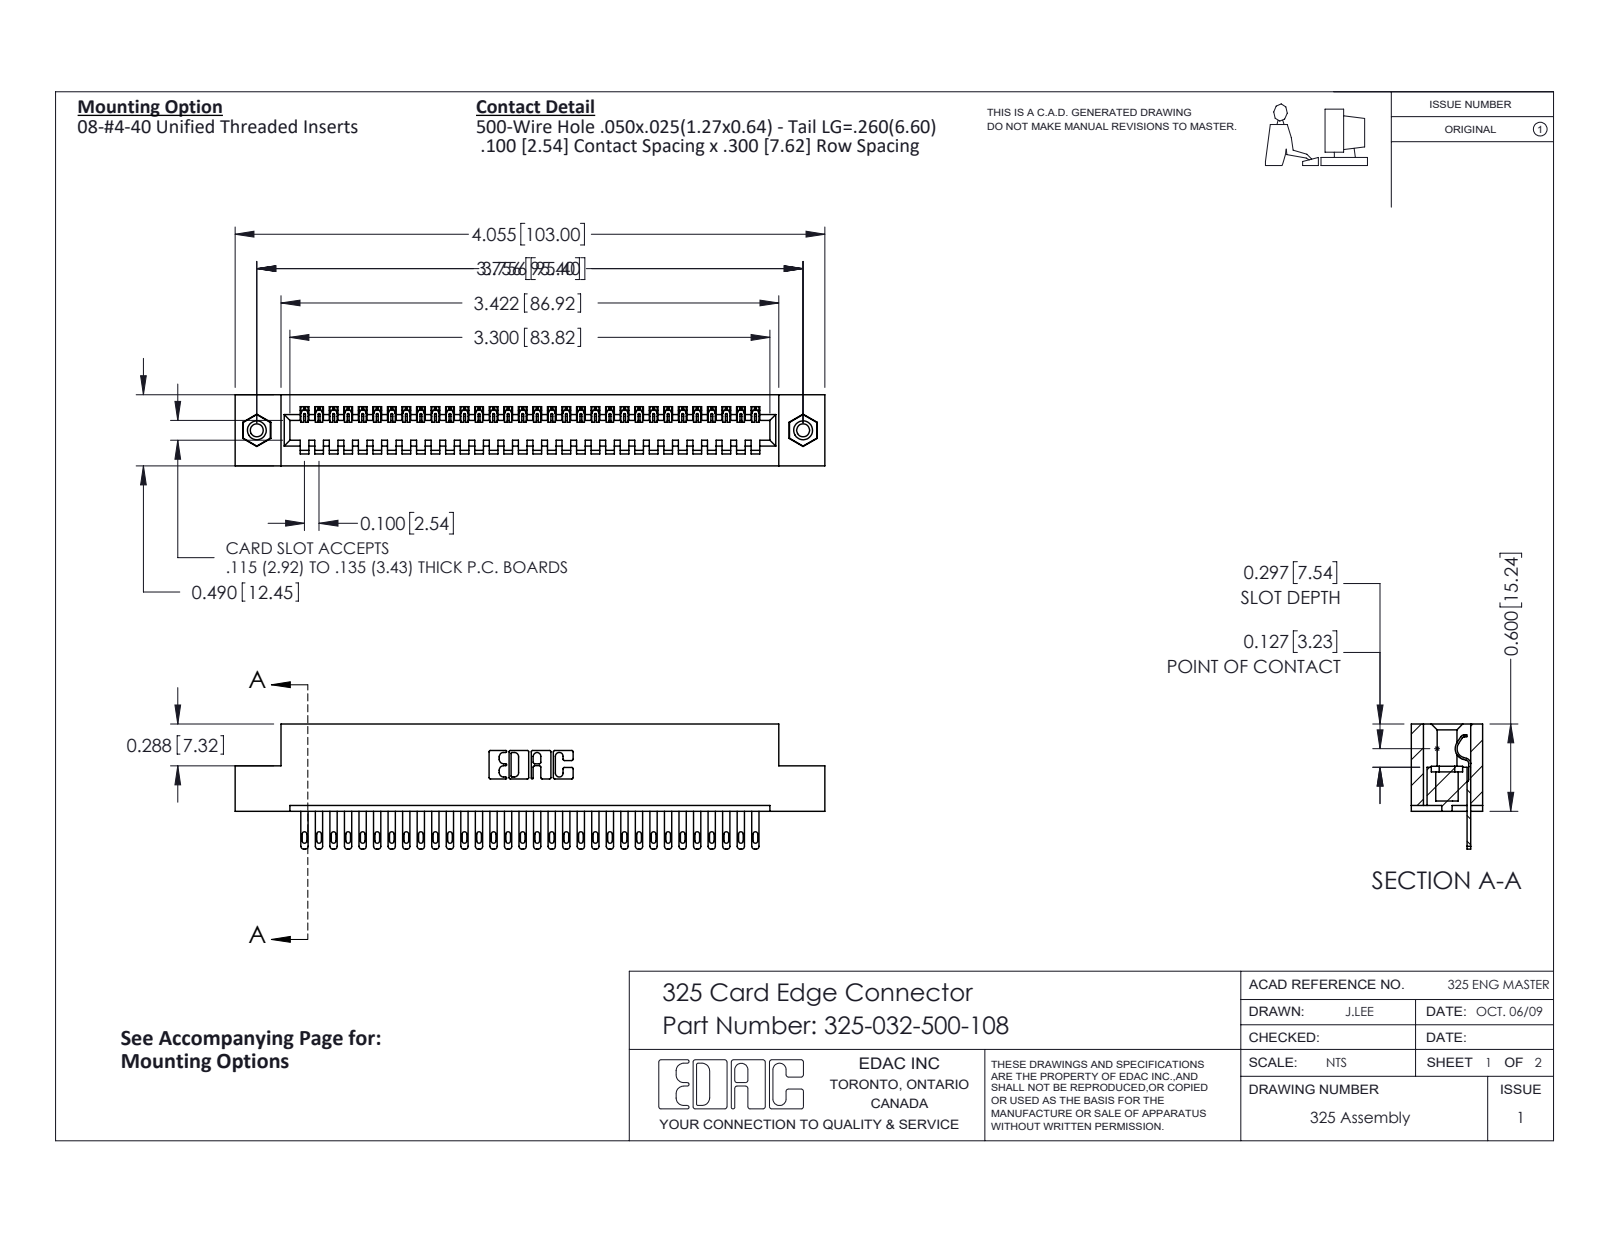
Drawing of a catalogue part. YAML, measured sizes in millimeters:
part_name: "325-292-001_325-293-100; 325-032-500-108; 345-250-001_345-250-003-102; 325 Part_TI"
step_written_by: "SolidWorks 2016 (CONFIG_CONTROL_DESIGN)"
units: millimeters
bodies: {solids: 35, faces: 1902, planar: 1254, cylindrical: 632, other: 16}
overall_size: [103, 21.8, 12.4]
volume: 13000
surface_area: 14140
round_holes:
  - {diameter: 2.3, count: 2}
  - {diameter: 3.2, count: 2}
  - {diameter: 4.1, count: 2}
round_bosses_or_shafts:
  - {diameter: 3.9, count: 2}
partial_cylinders:
  - {radius: 0.2, count: 64}
  - {radius: 0.4, count: 64}
  - {radius: 0.5, count: 64}
  - {radius: 0.3, count: 22}
  - {radius: 0.2, count: 6}
  - {radius: 0.8, count: 6}
  - {radius: 0.7, count: 3}
  - {radius: 0.4, count: 1}
face_to_face_distances: [2.1, 10.3, 7.6, 12.4, 2.7, 9.7, 0.6, 8.3, 1, 2.5]
hole_center_spacings: [95.4]
